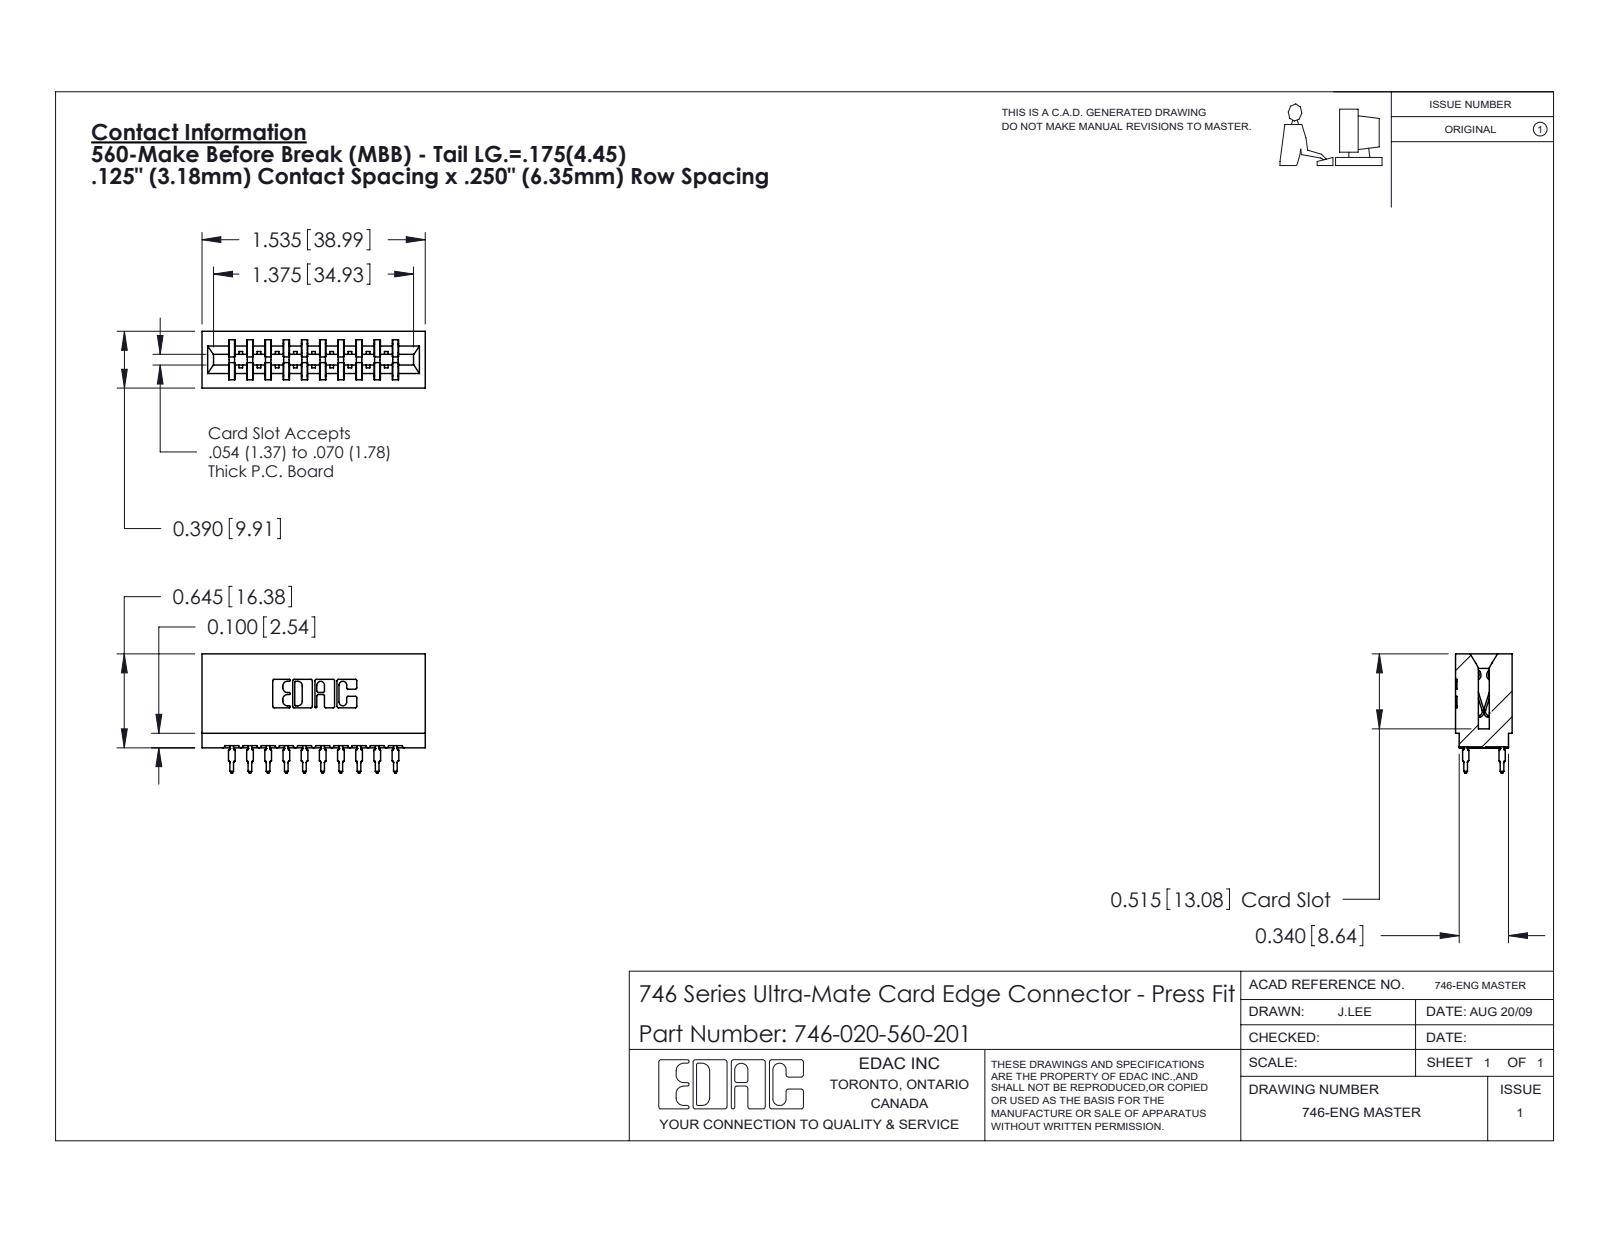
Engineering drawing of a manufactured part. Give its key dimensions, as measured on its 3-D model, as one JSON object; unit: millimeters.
{"part_name": "746-020-560-201; 746 Part_.515 Slot Depth - 01; 746-292-001_560", "step_written_by": "SolidWorks 2020 (CONFIG_CONTROL_DESIGN)", "units": "millimeters", "bodies": {"solids": 21, "faces": 1987, "planar": 995, "cylindrical": 472, "other": 520}, "overall_size": [39, 20.8, 9.9], "volume_mm3": 4460, "surface_area_mm2": 6897, "partial_cylinders_radius": [[0.5, 40], [0.3, 22], [0.4, 11], [0.1, 8], [0.3, 8], [0.2, 6], [0.8, 6], [0.5, 4]], "face_to_face_distances": [6.4, 8.5, 12.7, 1.4, 3.2, 1.1, 9.5, 5.3, 3.2, 9.9]}
